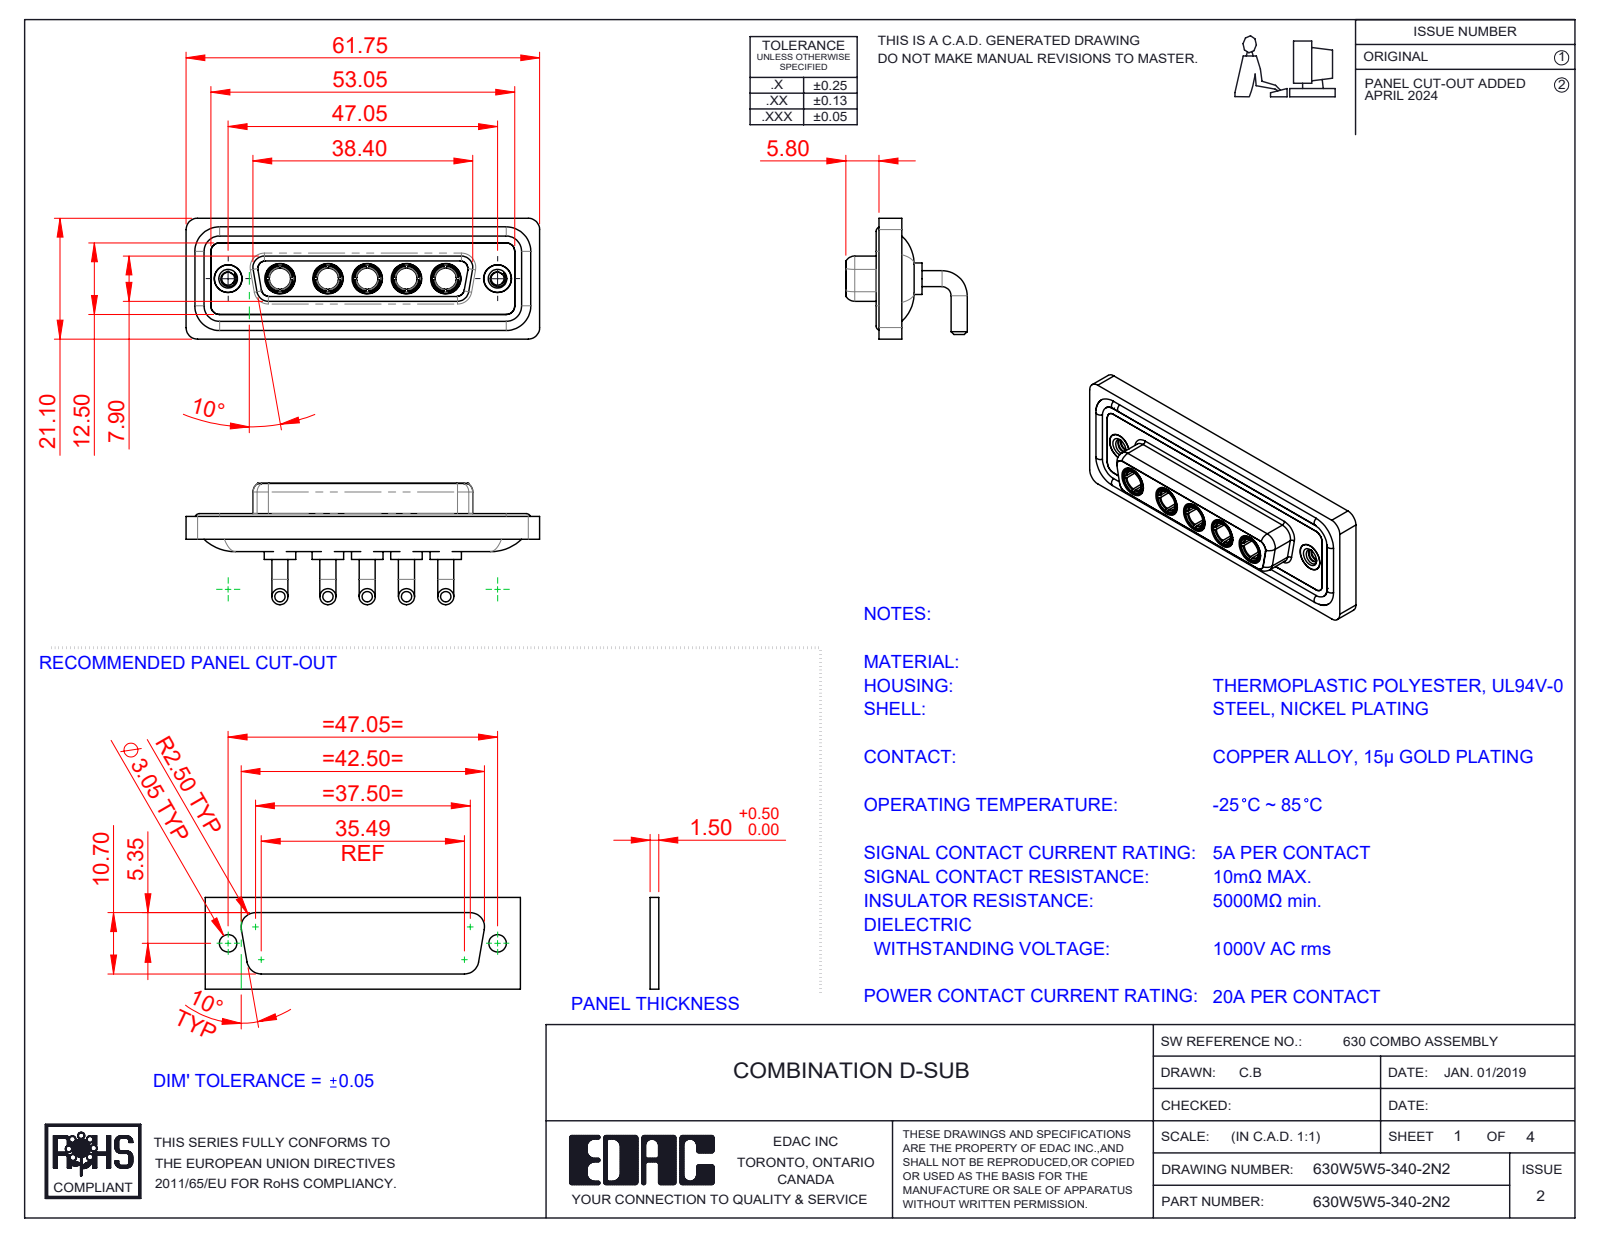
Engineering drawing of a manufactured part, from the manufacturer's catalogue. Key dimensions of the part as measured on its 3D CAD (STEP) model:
Part name (STEP PRODUCT): 630Combo Waterproof Housing_25 Contacts; 630Combo Shell Front_25 Contacts; 630Combo Housing_5W5; 630W5W5-340-2N2 (+3 more)
STEP written by: SolidWorks 2023 (CONFIG_CONTROL_DESIGN)
Units: millimetres
Bodies: 17 solids, 776 faces (250 planar, 313 cylindrical, 213 other)
Overall size (bounding box): 61.75 × 21.2 × 21.1
Volume: 8 435 mm³ · Surface area: 13 813 mm²
Round holes (diameter × count): ⌀4.85 ×7, ⌀3.7 ×5, ⌀5.3 ×5, ⌀2.26 ×2, ⌀4 ×2, ⌀4.05 ×2, ⌀5 ×2
Round bosses / shafts (diameter × count): ⌀2.8 ×10, ⌀5.5 ×5, ⌀5.2 ×5, ⌀4.96 ×5, ⌀4.75 ×5, ⌀3.75 ×5, ⌀1.6 ×4, ⌀4.95 ×2
Partial cylindrical surfaces — rounded edges, fillets, slot ends (radius × count): R1.5 ×18, R2 ×18, R1.35 ×8, R1.6 ×8, R2.1 ×5, R0.25 ×4, R0.5 ×4, R0.6 ×4
Main face-to-face distances: 0.4, 1.8, 4.1, 1.1, 1.5, 2.5, 3.1, 3.7, 1.6, 2.9
Hole centre spacings: 6.86, 9.04, 38.01, 6.87, 8.38, 13.72, 13.73, 15.25
